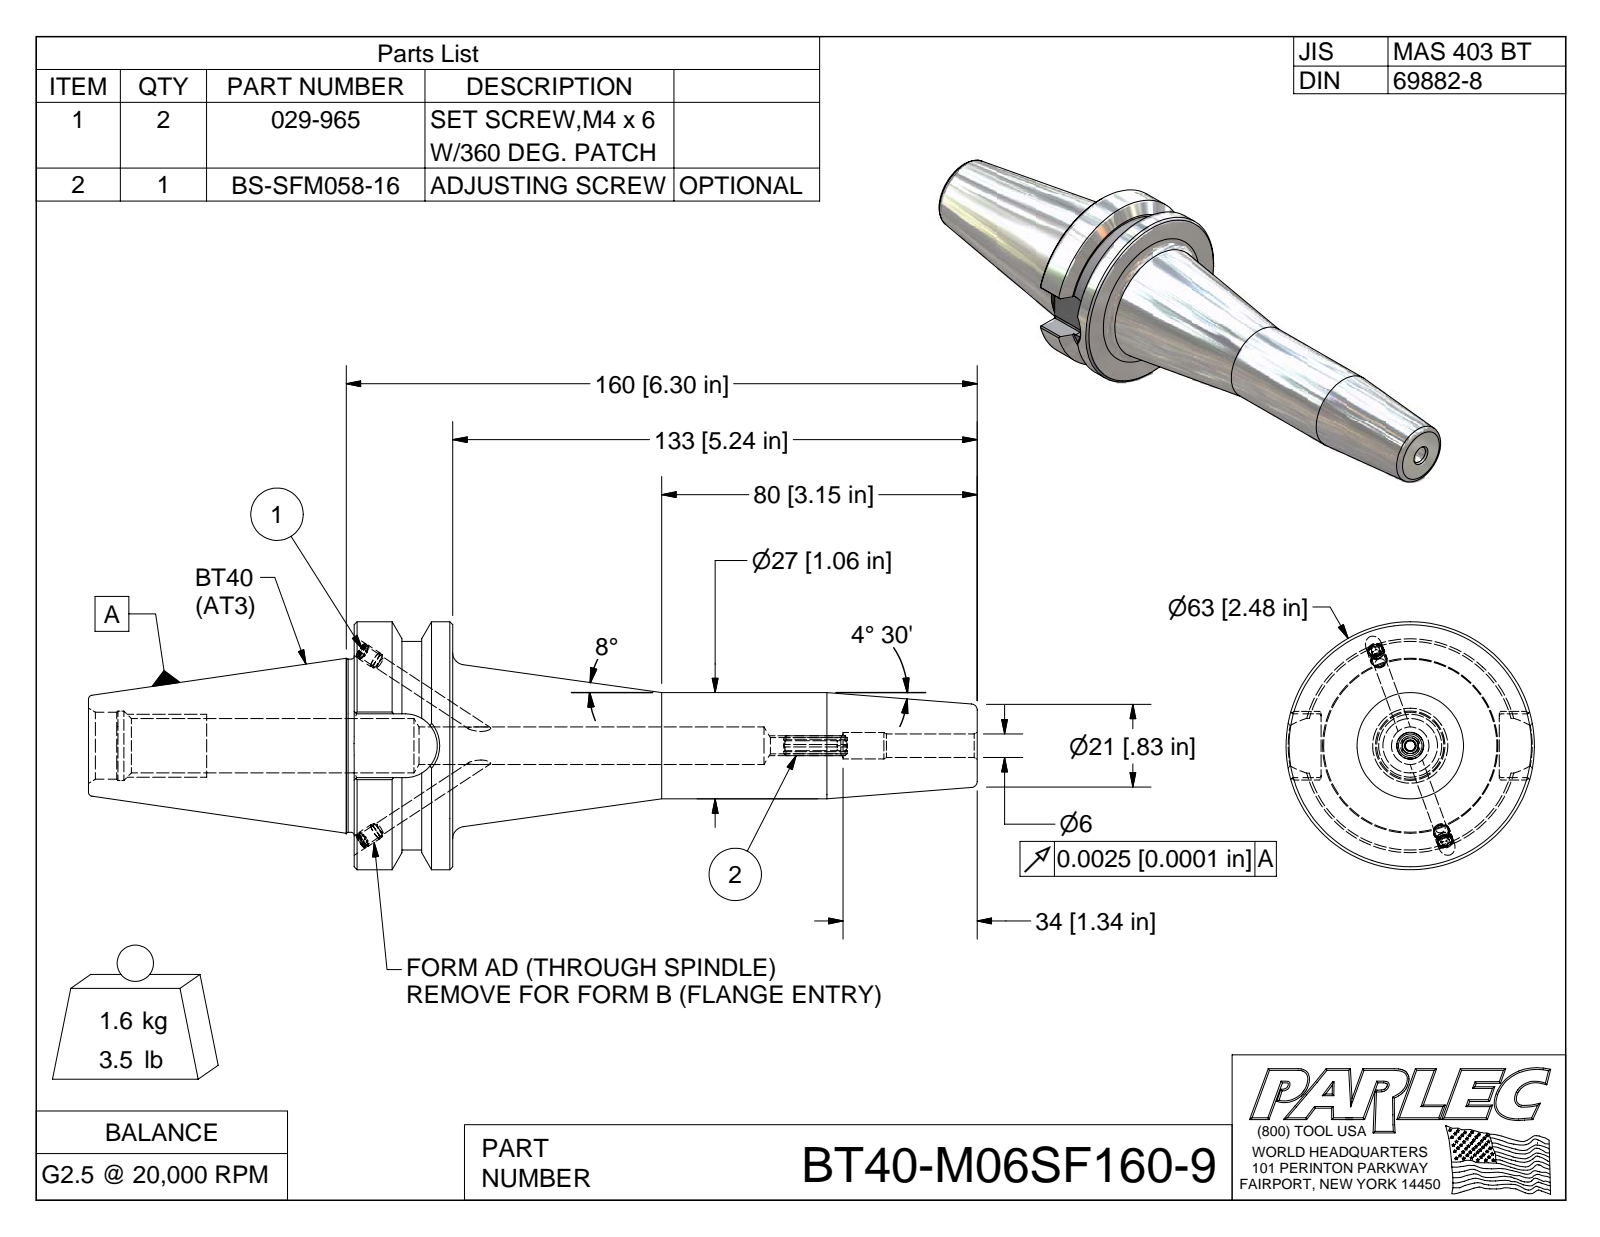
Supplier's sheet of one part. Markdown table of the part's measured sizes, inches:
| quantity | value |
| --- | --- |
| part name | BT40-M06SF160-9; BT40BC-M06SF160-9-1; 029-965; BS-SFM058-16 |
| STEP written by | Autodesk Inventor 2009 (AUTOMOTIVE_DESIGN) |
| units | inches |
| bodies | 4 solids, 134 faces (57 planar, 33 cylindrical, 44 other) |
| overall size | 8.874 × 2.48 × 2.48 |
| volume | 12.48 in³ |
| surface area | 59.04 in² |
| round holes (diameter × count) | 0.13 × 2, 0.161 × 2, 0.236 × 1, 0.266 × 1, 0.694 × 1 |
| round bosses / shafts (diameter × count) | 0.165 × 2, 0.157 × 2, 2.48 × 1, 2.087 × 1, 1.75 × 1, 1.73 × 1, 1.063 × 1 |
| partial cylindrical surfaces (radius × count) | 0.02 × 8, 0.098 × 1, 0.319 × 1 |
| main face-to-face distances | 0.984, 1.78, 6.221, 5.237, 2.653, 3.637, 8.874, 0.637, 0.811, 0.969 |
